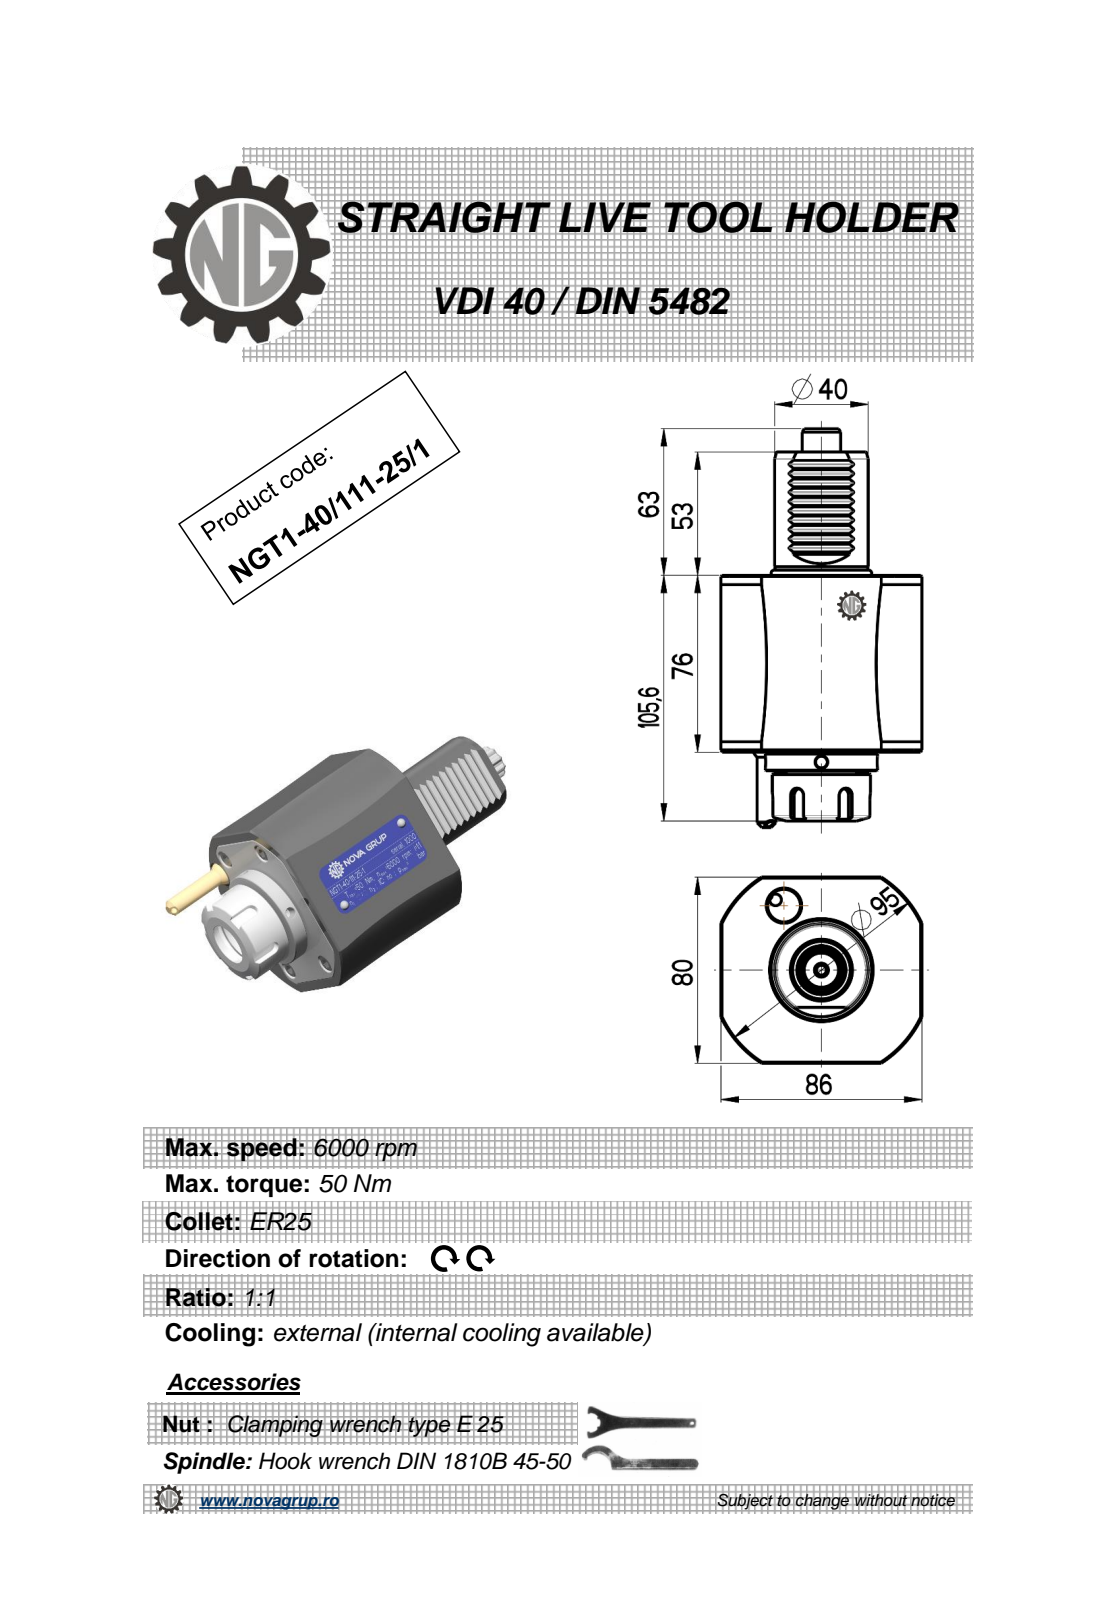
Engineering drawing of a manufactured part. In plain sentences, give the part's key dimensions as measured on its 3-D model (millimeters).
The part is named "NGT1_40_111_25_1". Its 3-D file was written by "PRO/ENGINEER BY PARAMETRIC TECHNOLOGY CORPORATION, 2010280 (CONFIG_CONTROL_DESIGN)". It is 1 solid with 313 faces: 96 planar, 95 cylindrical and 122 other. Overall it measures 171.34 by 86 by 81.6 millimeters. Its volume is 579 672 cubic millimeters and its surface area 50 588 square millimeters. Round holes: 3 of diameter 5, 1 of diameter 3, 1 of diameter 4.2, 1 of diameter 20.3. Round bosses or shafts: 1 of diameter 48, 1 of diameter 42, 1 of diameter 41.5, 1 of diameter 40, 1 of diameter 33, 1 of diameter 8. Partial cylindrical surfaces (rounded edges, fillets, slot ends): 18 of radius 3.03, 10 of radius 0.3, 6 of radius 0.22, 5 of radius 3, 1 of radius 6.75, 1 of radius 8.22, 1 of radius 47.5. The main face-to-face distances are 76, 80, 86, 84, 8, 53, 129, 137, 2.83, 5.66. The hole center spacings are 40.
